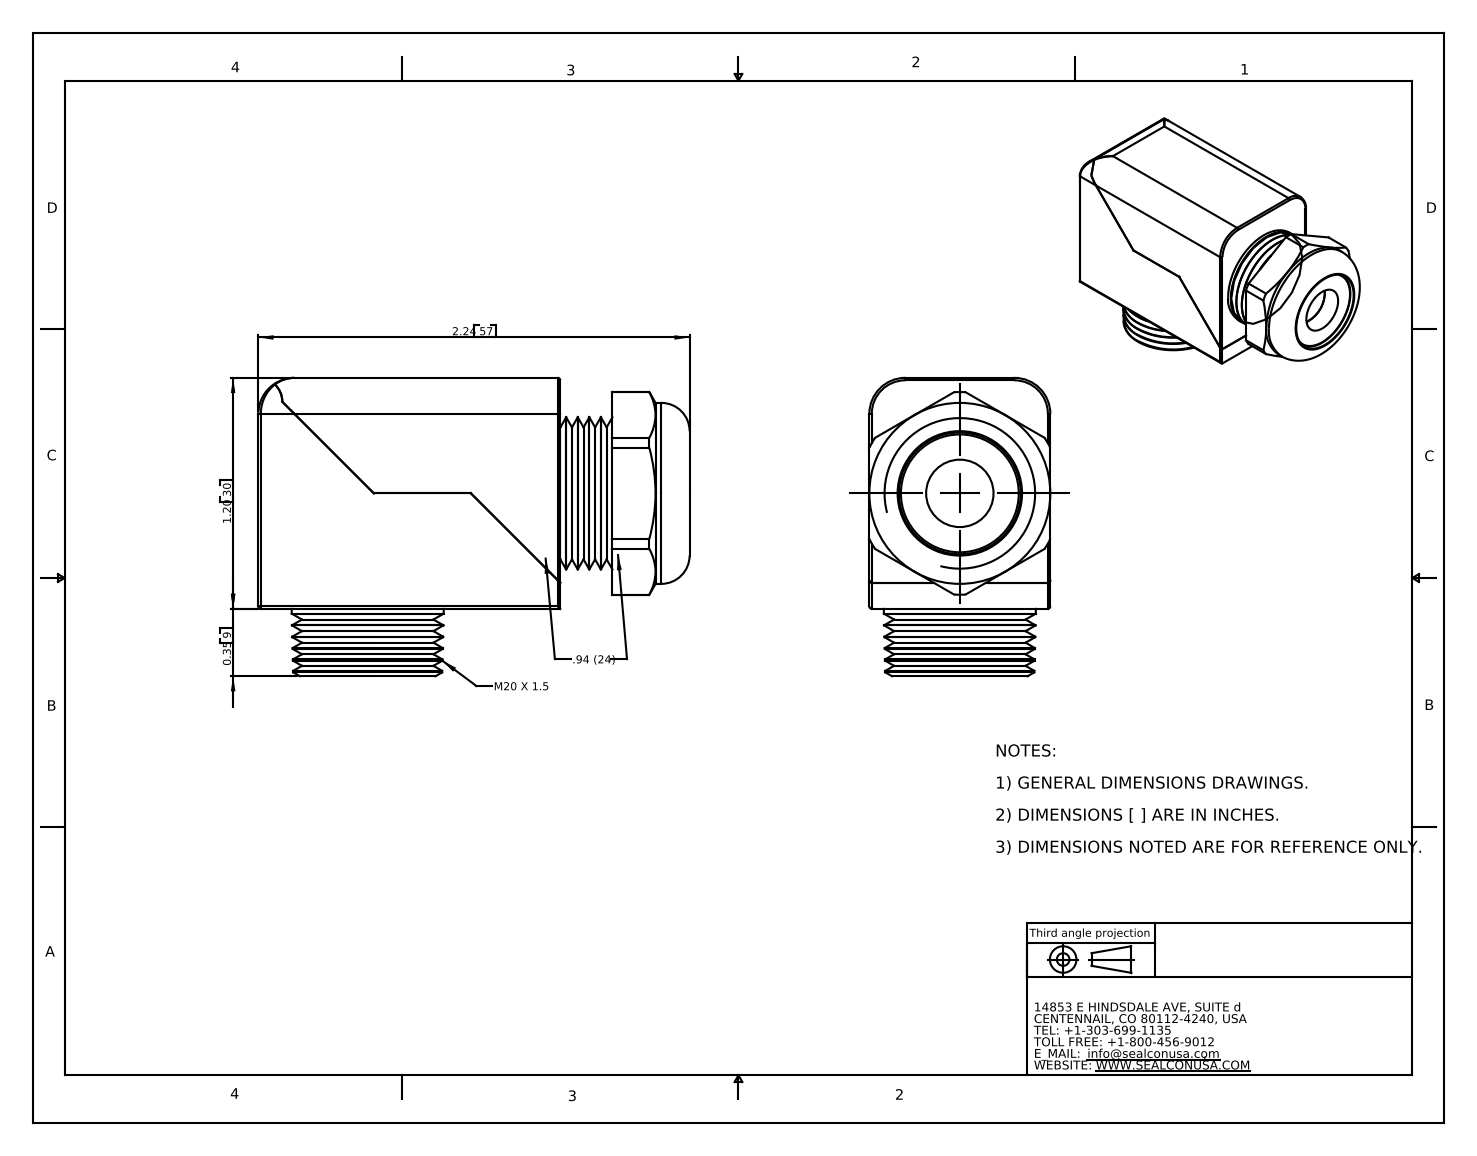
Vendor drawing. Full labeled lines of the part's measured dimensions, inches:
Part name (STEP PRODUCT): ED20MR-BK
STEP written by: SolidWorks 2007 (CONFIG_CONTROL_DESIGN)
Units: inches
Bodies: 3 solids, 151 faces (29 planar, 48 cylindrical, 74 other)
Overall size (bounding box): 2.24 × 1.55 × 0.94
Volume: 2.022 in³ · Surface area: 19.72 in²
Round holes (diameter × count): ⌀0.35 ×2, ⌀0.632 ×1
Round bosses / shafts (diameter × count): ⌀0.94 ×1, ⌀0.79 ×1
Partial cylindrical surfaces — rounded edges, fillets, slot ends (radius × count): R0.013 ×8, R0.187 ×3, R0.124 ×1, R0.526 ×1
Main face-to-face distances: 0.94, 0.6, 0.356, 1.2, 1.568, 0.495, 2.063, 0.224, 0.271, 1.839
